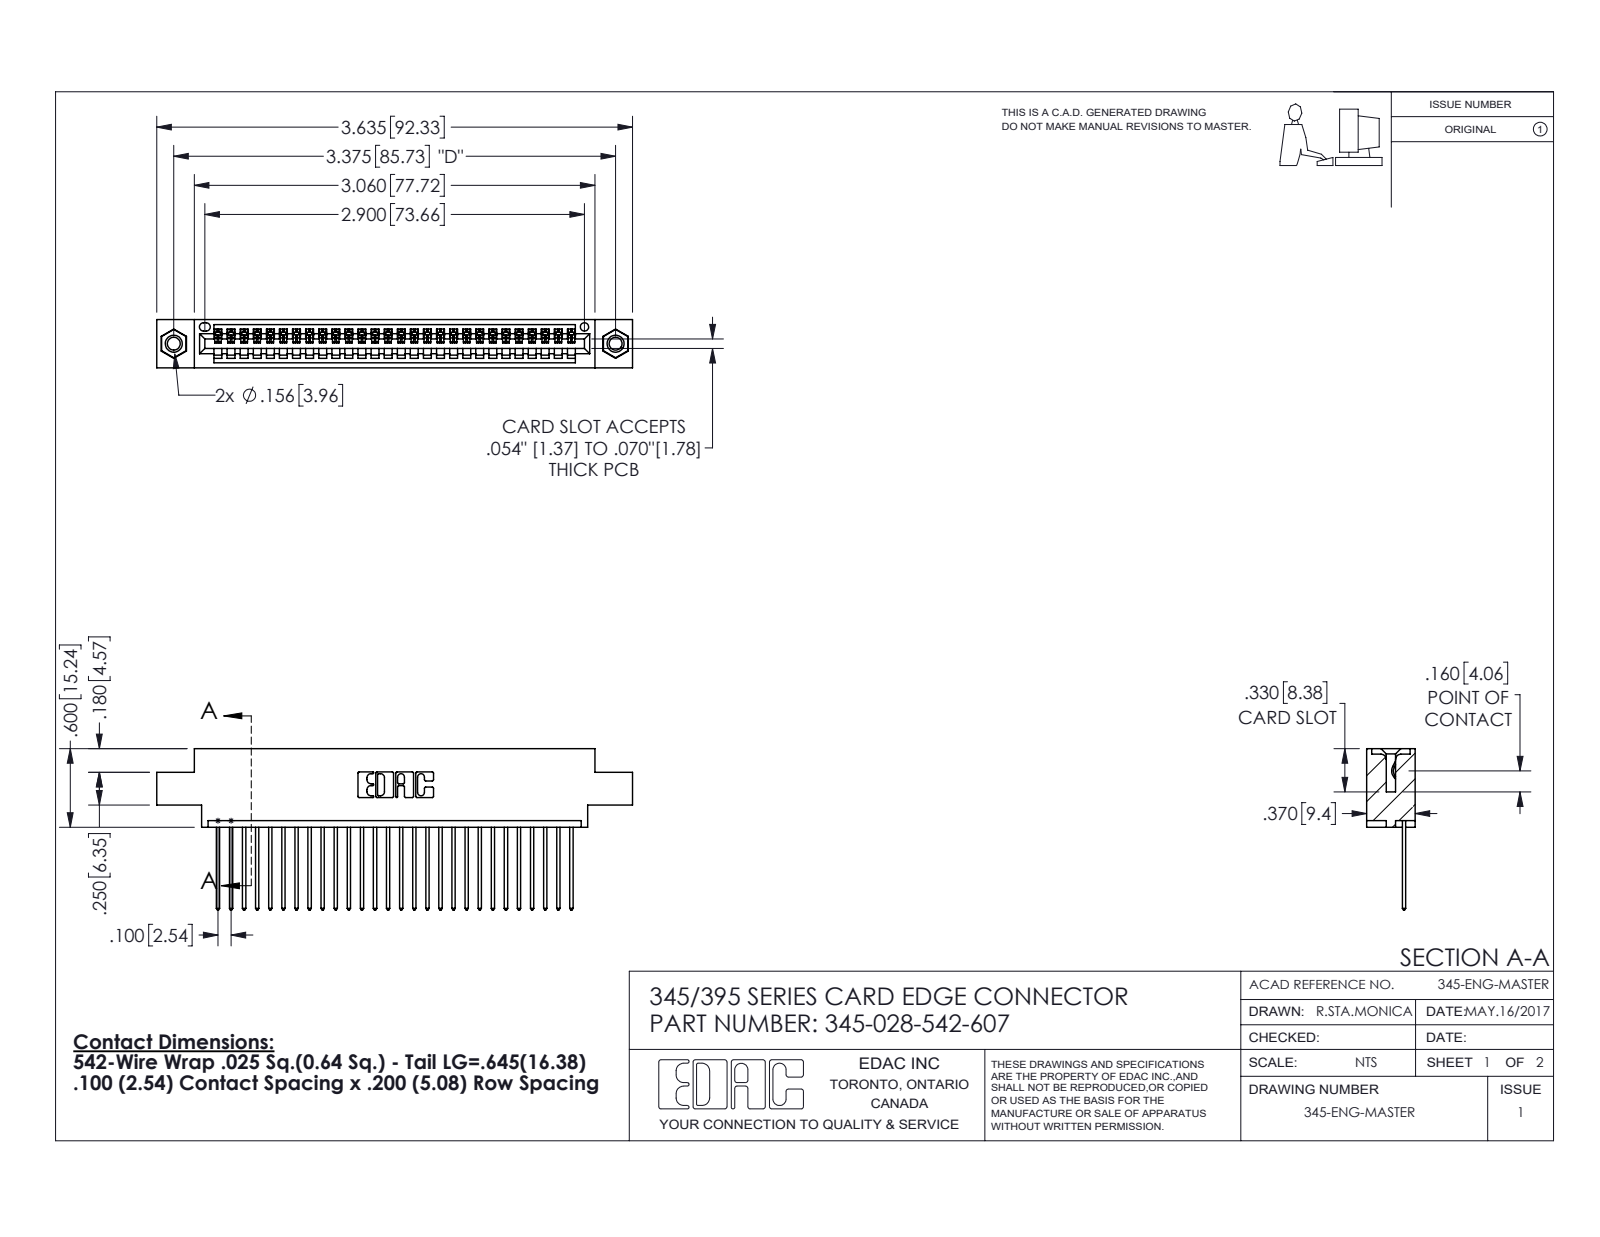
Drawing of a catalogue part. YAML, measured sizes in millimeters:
part_name: "345 Part_0.170 Offset - 0.156 Dia-TI; 345-292-001_345-293-142; 345-250-001_345-250-005-103; 345-028-542-607"
step_written_by: "SolidWorks 2016 (CONFIG_CONTROL_DESIGN)"
units: millimeters
bodies: {solids: 31, faces: 1814, planar: 1236, cylindrical: 562, other: 16}
overall_size: [92.3, 31.3, 9.4]
volume: 8590
surface_area: 11780
round_holes:
  - {diameter: 2.5, count: 2}
  - {diameter: 3.2, count: 2}
  - {diameter: 4, count: 2}
  - {diameter: 1.6, count: 1}
round_bosses_or_shafts:
  - {diameter: 3.9, count: 2}
partial_cylinders:
  - {radius: 0.2, count: 56}
  - {radius: 0.3, count: 56}
  - {radius: 0.3, count: 22}
  - {radius: 0.2, count: 6}
  - {radius: 0.8, count: 6}
  - {radius: 0.7, count: 3}
  - {radius: 0.8, count: 2}
  - {radius: 1, count: 2}
face_to_face_distances: [1.8, 7.6, 9.4, 2.5, 6.9, 0.6, 5.1, 5.7, 4.4, 3.8]
hole_center_spacings: [6.9, 79.8, 85.7]
